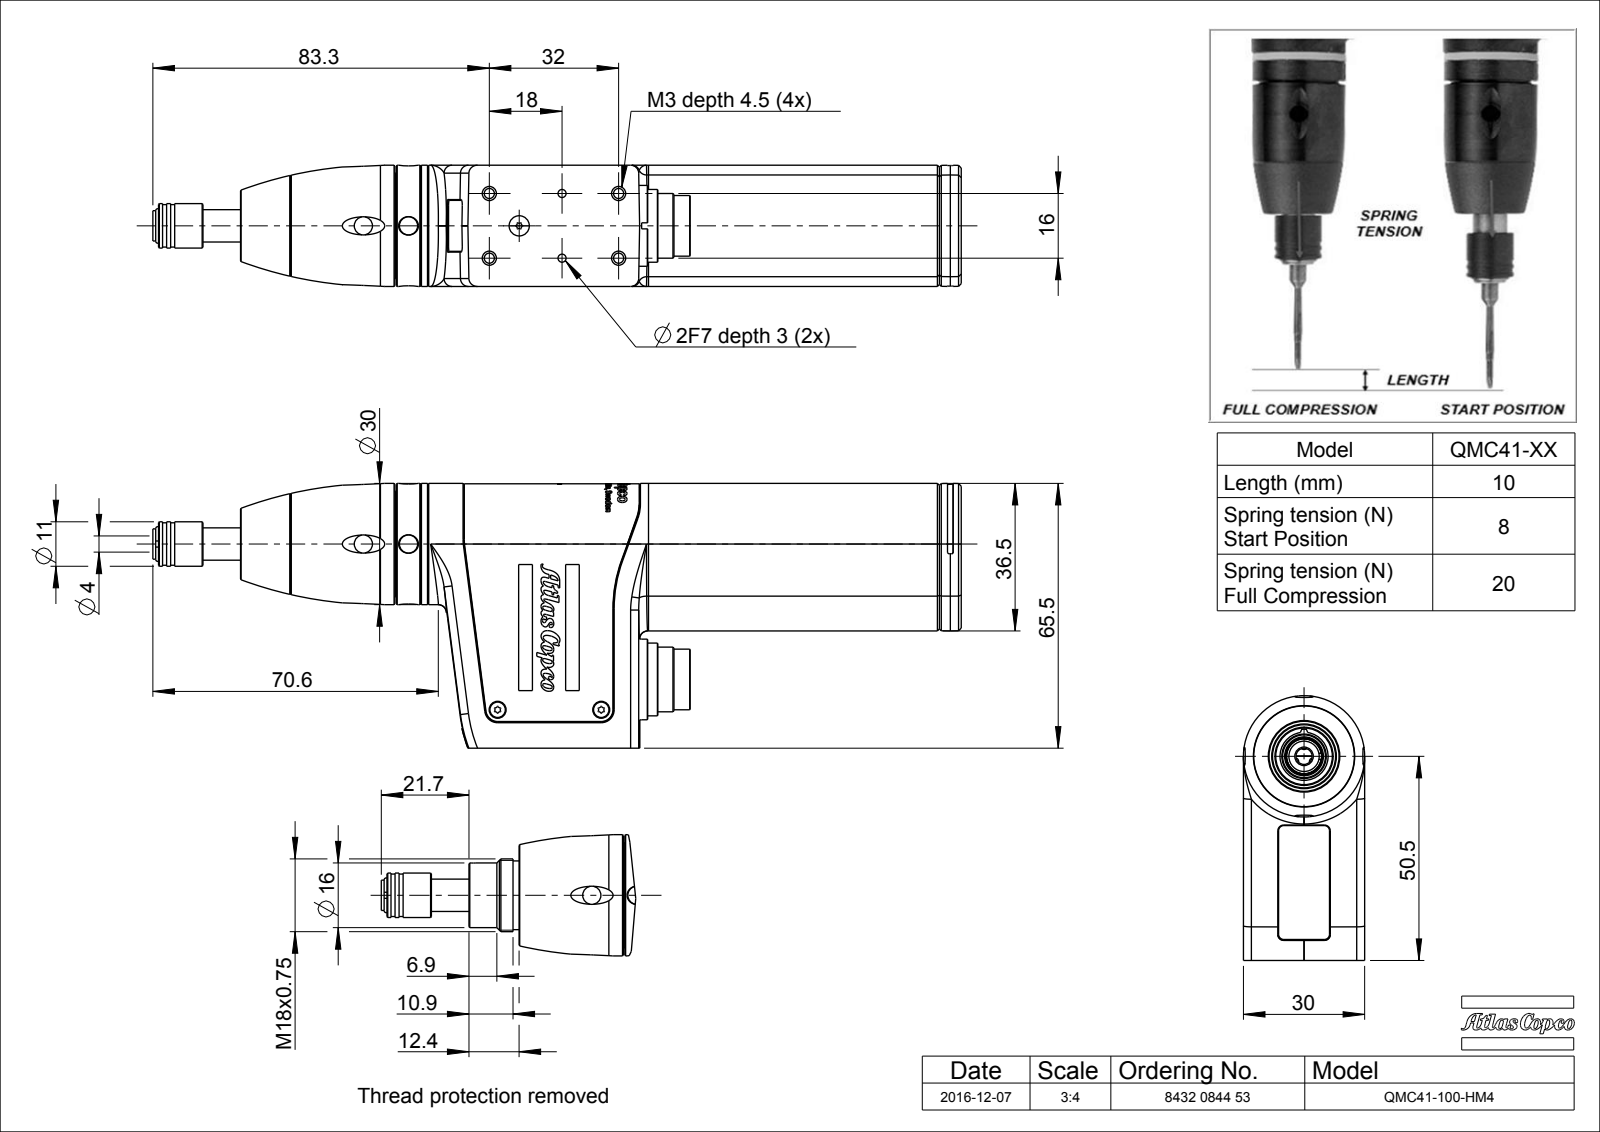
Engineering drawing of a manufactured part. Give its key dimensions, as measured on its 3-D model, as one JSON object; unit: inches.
{"part_name": "4216253400; 4216253600; 4216256600; 0993000295_SPEC_3 (+8 more)", "step_written_by": "CREO PARAMETRIC BY PTC INC, 2016260 (CONFIG_CONTROL_DESIGN)", "units": "inches", "bodies": {"solids": 22, "faces": 1494, "planar": 369, "cylindrical": 630, "other": 495}, "overall_size": [7.877, 2.579, 1.181], "volume_in3": 3.751, "surface_area_in2": 98.42, "round_holes": [[0.079, 6], [0.063, 4], [0.098, 4], [0.177, 4], [0.067, 3], [0.083, 3], [0.087, 3], [0.039, 2], [0.047, 2], [0.081, 2], [0.106, 2], [0.551, 2]], "round_bosses_or_shafts": [[0.039, 12], [0.028, 12], [0.024, 12], [0.15, 4], [0.787, 2], [0.709, 2], [0.079, 2], [1.181, 1]], "partial_cylinders_radius": [[0.079, 36], [0.008, 28], [0.004, 12], [0.007, 12], [0.013, 12], [0.021, 12], [0.016, 8], [0.059, 8]], "face_to_face_distances": [0.028, 1.146, 1.173, 1.118, 0.031, 1.15, 1.177, 0.079, 0.138, 1.181], "hole_center_spacings": [0.63, 0.689, 0.429, 0.44, 0.523, 0.551, 0.614, 0.64]}
